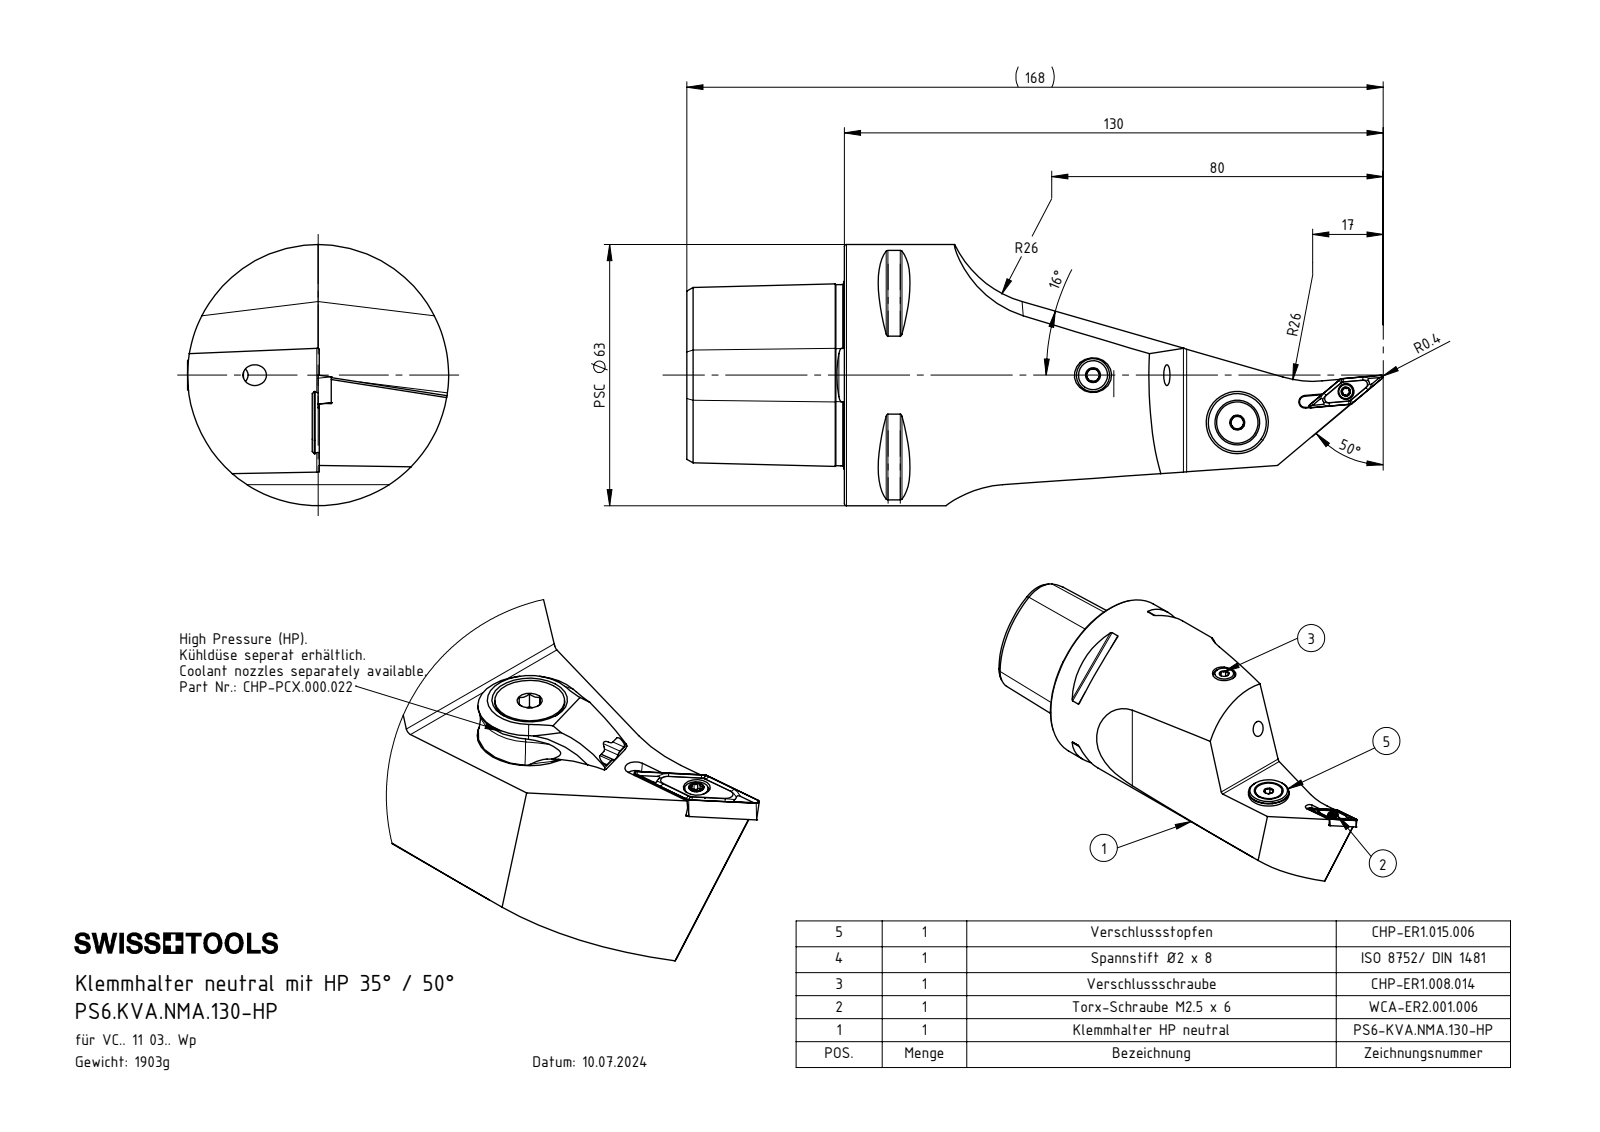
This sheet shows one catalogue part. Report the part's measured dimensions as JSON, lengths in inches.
{"part_name": "CHP-PCX.000.022_B; VCGT110304; DIN 3771 - 6.5x1.5; PS6-KVA.NMA.130-HP_A (+7 more)", "step_written_by": "SolidWorks 2022 (AUTOMOTIVE_DESIGN)", "units": "inches", "bodies": {"solids": 9, "faces": 477, "planar": 104, "cylindrical": 134, "other": 239}, "overall_size": [6.614, 2.48, 2.48], "volume_in3": 14.81, "surface_area_in2": 60.94, "round_holes": [[0.165, 2], [0.197, 2], [0.047, 1], [0.079, 1], [0.081, 1], [0.11, 1], [0.118, 1], [0.152, 1], [0.209, 1], [0.276, 1], [0.319, 1], [0.335, 1]], "round_bosses_or_shafts": [[2.48, 1], [0.585, 1], [0.528, 1], [0.394, 1], [0.315, 1], [0.217, 1], [0.197, 1], [0.134, 1]], "partial_cylinders_radius": [[0.02, 10], [0.039, 7], [0.008, 6], [0.014, 5], [0.236, 4], [1.024, 4], [0.043, 2], [0.047, 2]], "face_to_face_distances": [1.496, 0.98, 0.433, 1.063, 2.197, 0.189, 0.059, 1.488, 0.425, 0.076], "hole_center_spacings": [0.177, 0.941, 0.944, 1.072, 1.075, 1.083, 1.443, 1.503]}
